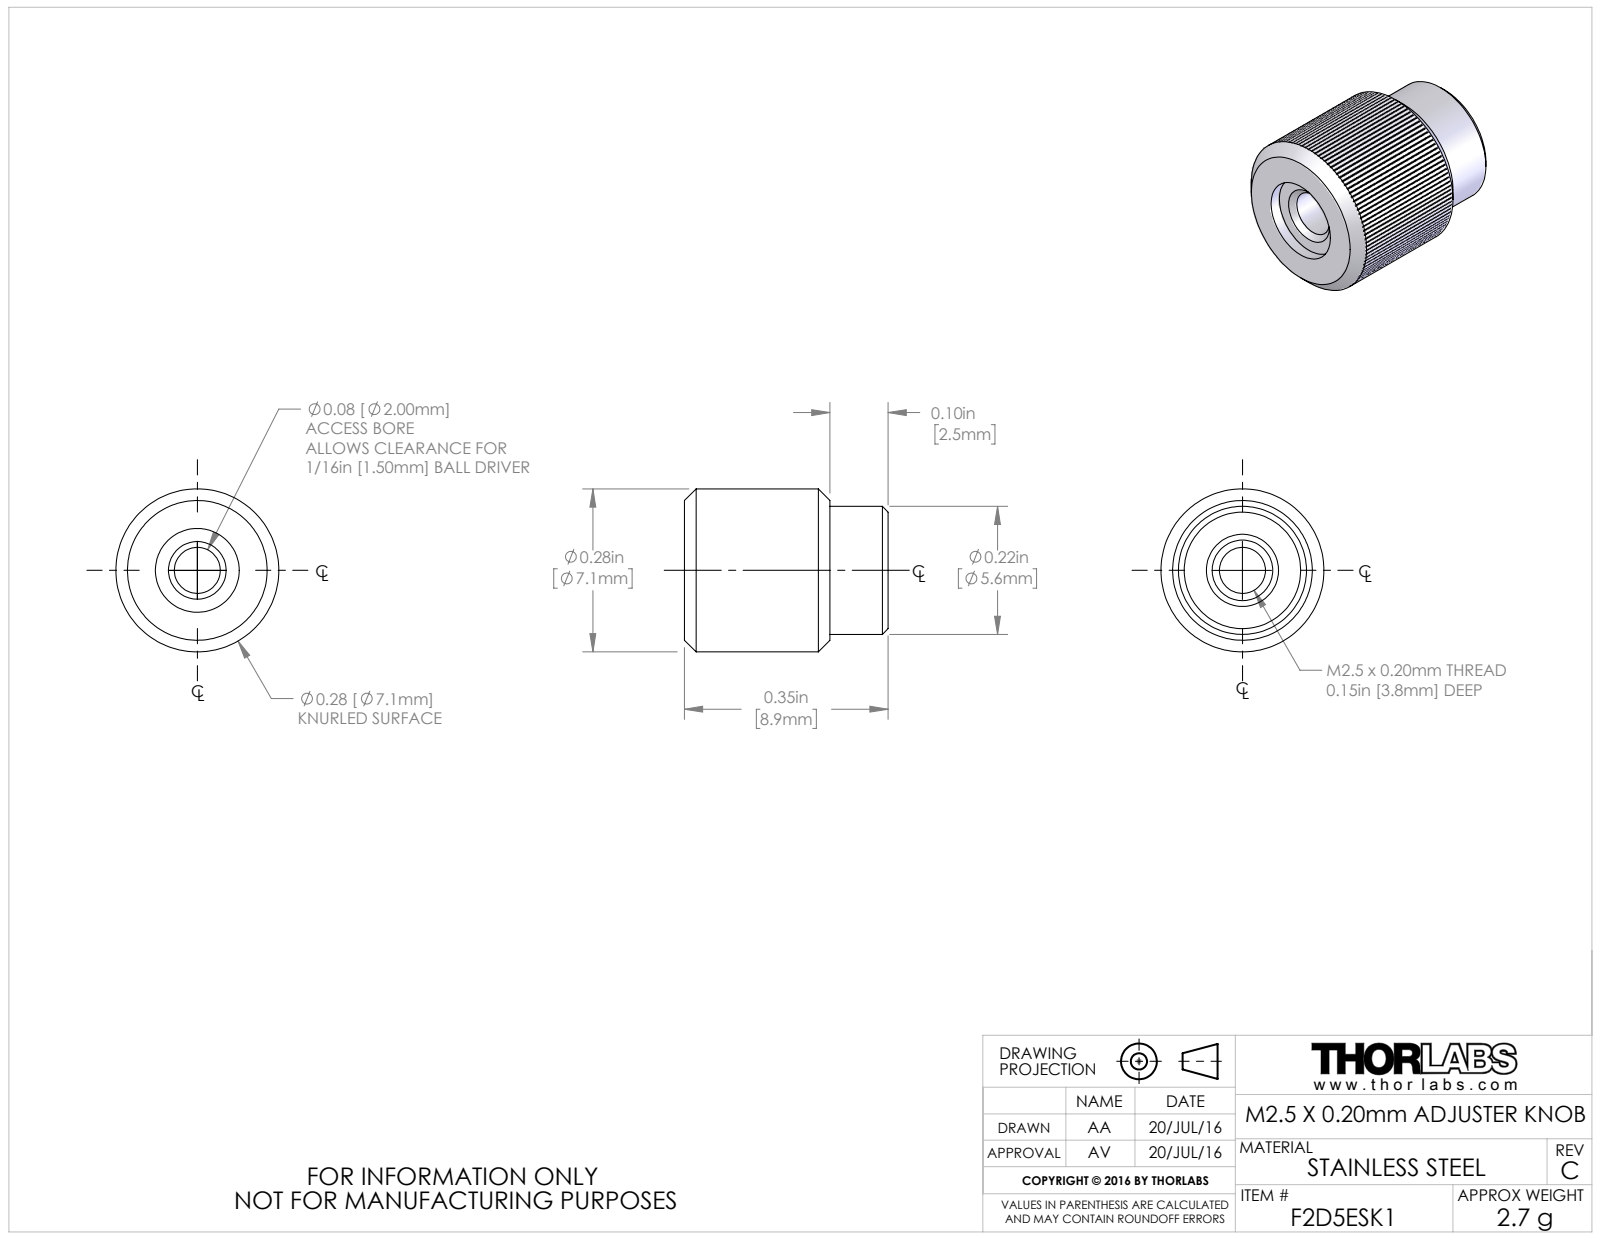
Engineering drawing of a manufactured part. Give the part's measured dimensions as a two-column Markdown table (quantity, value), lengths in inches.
| quantity | value |
| --- | --- |
| part name | 7658-E0W |
| STEP written by | SolidWorks 2011 (AUTOMOTIVE_DESIGN) |
| units | inches |
| bodies | 1 solid, 19 faces (3 planar, 8 cylindrical, 8 other) |
| overall size | 0.35 × 0.28 × 0.28 |
| volume | 0.016 in³ |
| surface area | 0.464 in² |
| round holes (diameter × count) | 0.079 × 1, 0.098 × 1 |
| round bosses / shafts (diameter × count) | 0.28 × 1, 0.22 × 1 |
| main face-to-face distances | 0.35, 0.15, 0.2 |
